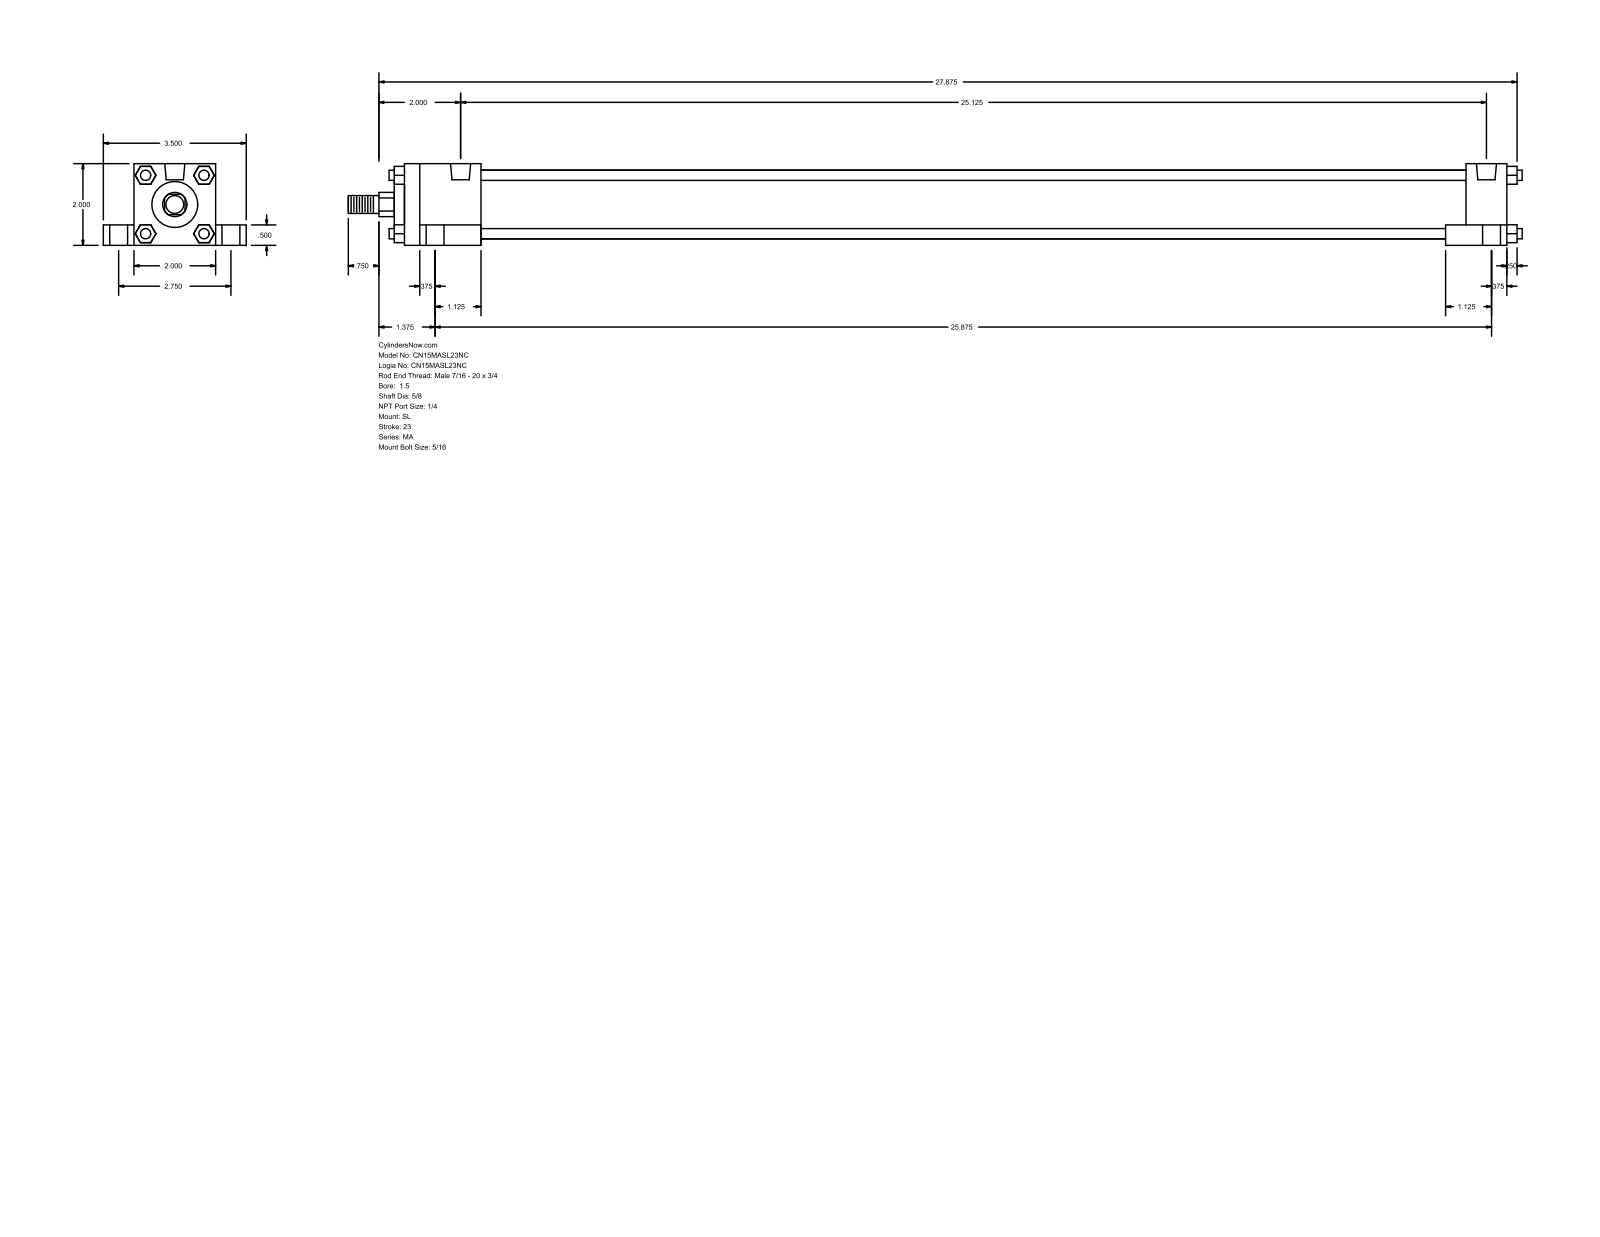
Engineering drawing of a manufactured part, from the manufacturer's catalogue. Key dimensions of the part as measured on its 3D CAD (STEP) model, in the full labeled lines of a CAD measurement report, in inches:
Part name (STEP PRODUCT): MA_SL__0150_0.625
STEP written by: GSSL Pune (CONFIG_CONTROL_DESIGN)
Units: inches
Bodies: 0 solids, 148 faces (112 planar, 36 cylindrical, 0 other)
Overall size (bounding box): 28.75 × 3.5 × 2
Round holes (diameter × count): ⌀0.313 ×4, ⌀0.437 ×4, ⌀0.687 ×4, ⌀0.492 ×2
Round bosses / shafts (diameter × count): ⌀0.25 ×4, ⌀1.69 ×1, ⌀1.125 ×1, ⌀0.625 ×1, ⌀0.437 ×1
Partial cylindrical surfaces — rounded edges, fillets, slot ends (radius × count): R0.297 ×1
Main face-to-face distances: 2, 0.75, 1.5, 2.75, 0.5, 27, 24.125, 1, 0.25, 0.375
Hole centre spacings: 1.38, 1.51, 2.75, 25.125, 25.287, 25.787, 25.875, 26.021
